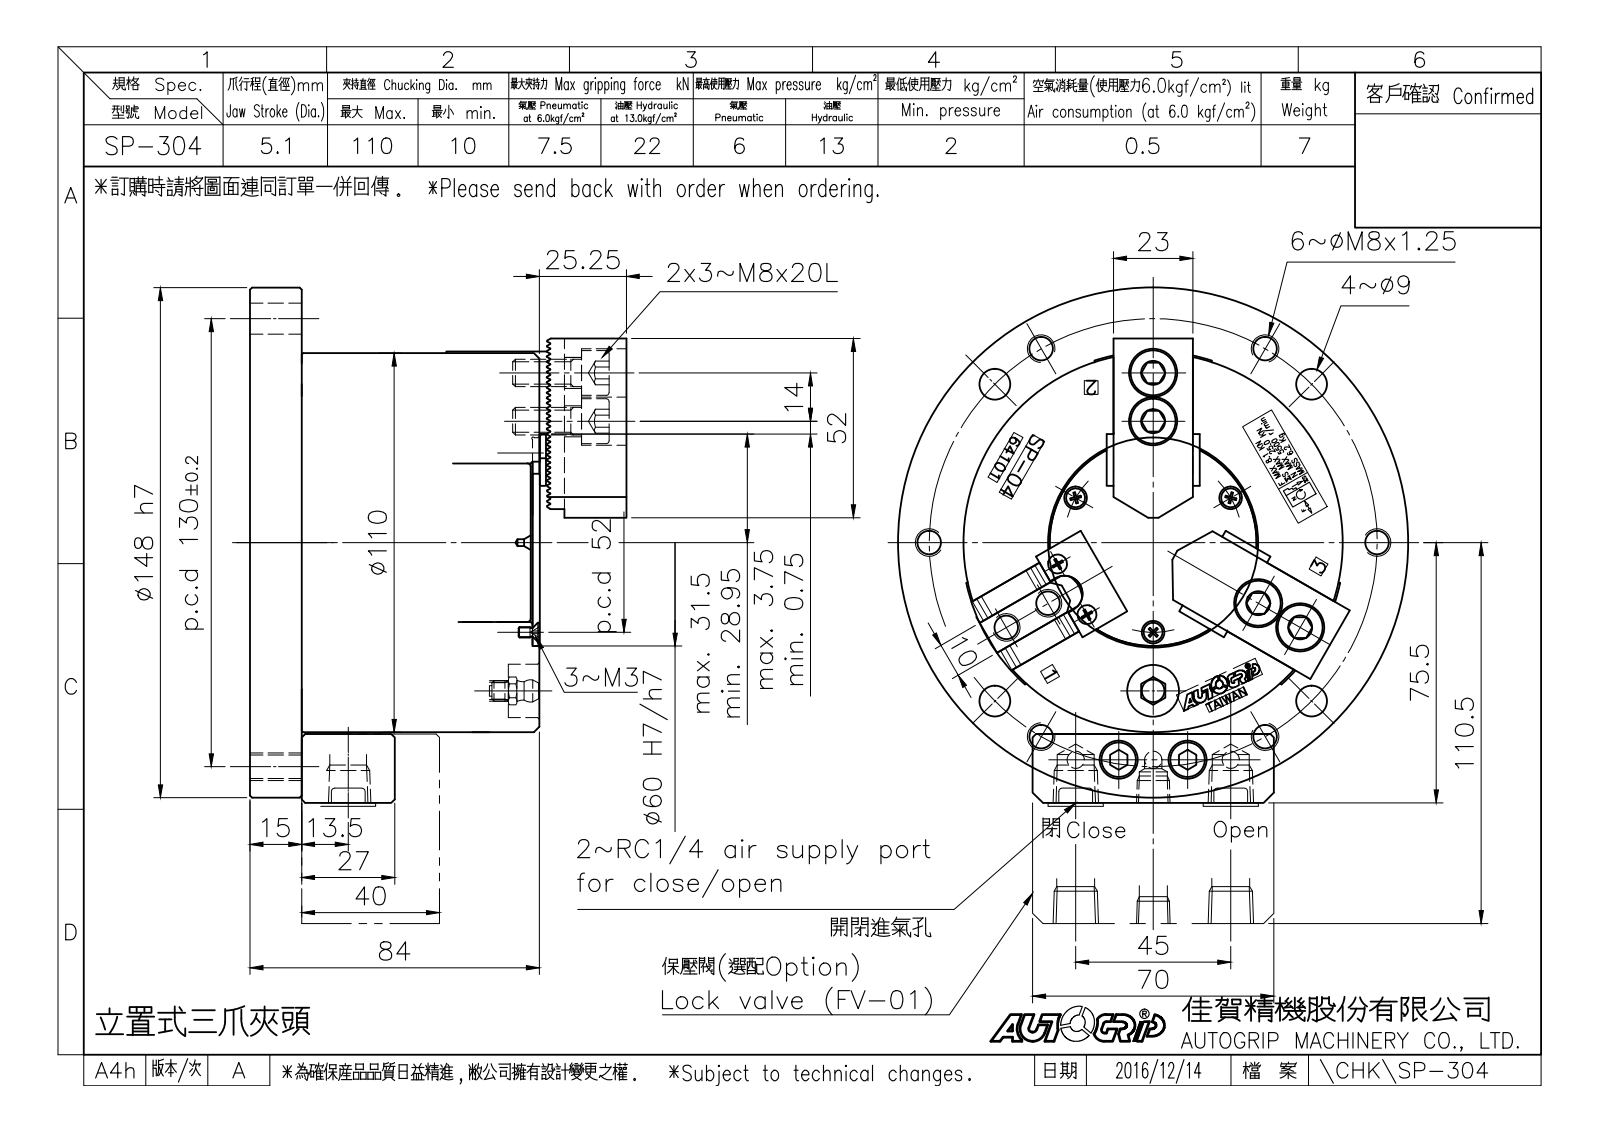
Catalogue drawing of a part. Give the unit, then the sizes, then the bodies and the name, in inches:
Units: inches
Overall size (bounding box): 5.898 × 5.827 × 4.301
Round holes (diameter × count): ⌀0.197 ×15, ⌀0.268 ×12, ⌀0.354 ×10, ⌀0.26 ×8, ⌀0.433 ×8, ⌀0.134 ×6, ⌀0.551 ×6, ⌀0.142 ×3, ⌀0.362 ×3, ⌀0.421 ×2, ⌀0.079 ×1, ⌀0.094 ×1
Round bosses / shafts (diameter × count): ⌀0.236 ×20, ⌀0.118 ×10, ⌀0.394 ×8, ⌀0.512 ×6, ⌀0.315 ×6, ⌀5.827 ×1, ⌀4.331 ×1, ⌀3.346 ×1
Partial cylindrical surfaces — rounded edges, fillets, slot ends (radius × count): R0.004 ×150, R0.207 ×6, R0.236 ×3, R2.165 ×3, R1.181 ×1
Main face-to-face distances: 0.591, 0.906, 0.65, 0.217, 1.122, 2.717, 0.866, 3.307, 0.256, 2.242
Hole centre spacings: 1.34, 1.929, 3.205, 2.559, 3.147, 4.339, 0.78, 0.839
Volume: 59.03 in³ · Surface area: 295.1 in²
Bodies: 44 solids, 2447 faces (1537 planar, 608 cylindrical, 302 other)
Part name (STEP PRODUCT): CF-SU-308-07000; CF-SP-304-02000; 圓頭內六角螺栓_M6x18; CF-SP-304-01000 (+8 more)
STEP written by: SolidWorks 2016 (CONFIG_CONTROL_DESIGN)
